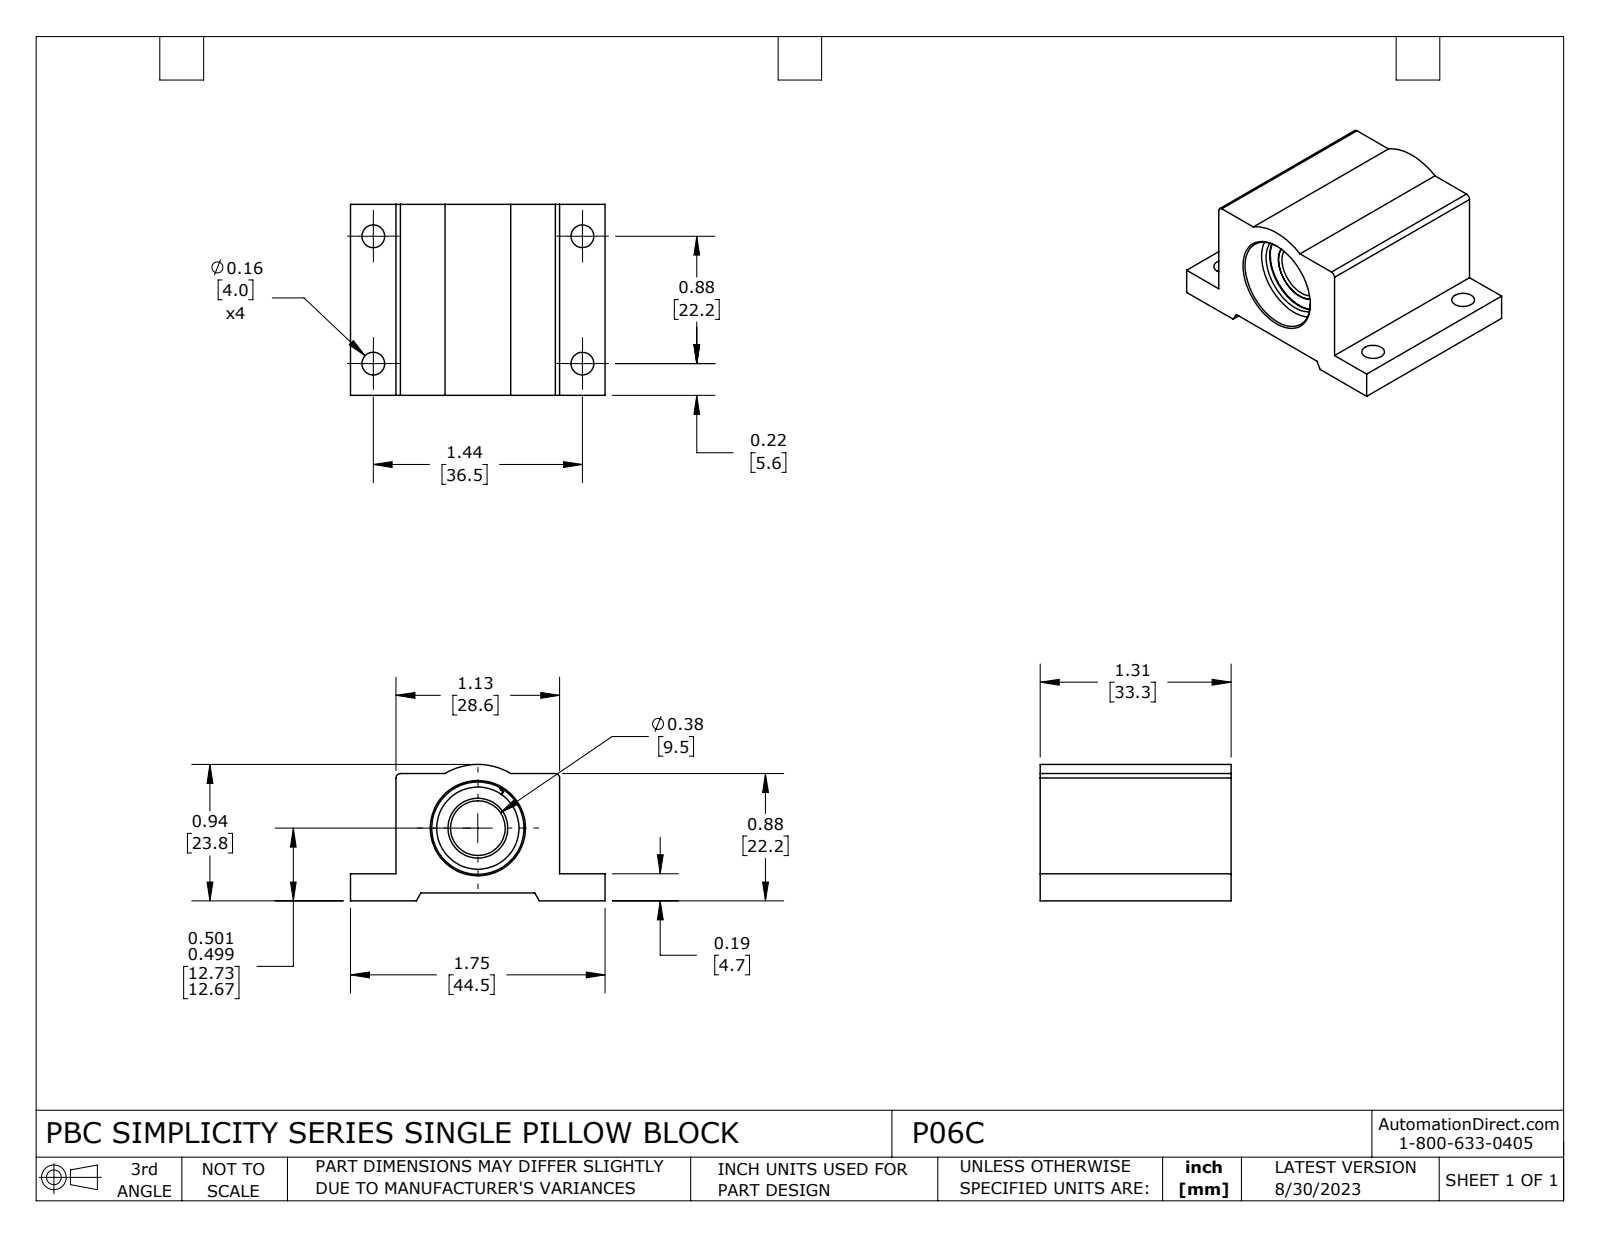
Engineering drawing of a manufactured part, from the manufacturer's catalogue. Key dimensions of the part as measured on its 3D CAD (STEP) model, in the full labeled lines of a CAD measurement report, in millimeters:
Part name (STEP PRODUCT): P06C
STEP written by: SolidWorks 2021 (CONFIG_CONTROL_DESIGN)
Units: millimetres
Bodies: 7 solids, 164 faces (45 planar, 71 cylindrical, 48 other)
Overall size (bounding box): 44.5 × 33.3 × 23.8
Volume: 18 880 mm³ · Surface area: 11 980 mm²
Round holes (diameter × count): ⌀4 ×4, ⌀9.6 ×1, ⌀10.4 ×1, ⌀14.4 ×1, ⌀16.1 ×1, ⌀16.9 ×1
Round bosses / shafts (diameter × count): ⌀17.1 ×1, ⌀15.8 ×1, ⌀14.9 ×1, ⌀13.3 ×1
Partial cylindrical surfaces — rounded edges, fillets, slot ends (radius × count): R0.2 ×4, R0.1 ×2, R0.4 ×2, R0.8 ×2, R11.1 ×1
Main face-to-face distances: 22.2, 1.4, 28.6, 20.8, 4.7, 3.4, 17.5, 33.4, 8, 36.5
Hole centre spacings: 22.2, 36.5, 42.7
